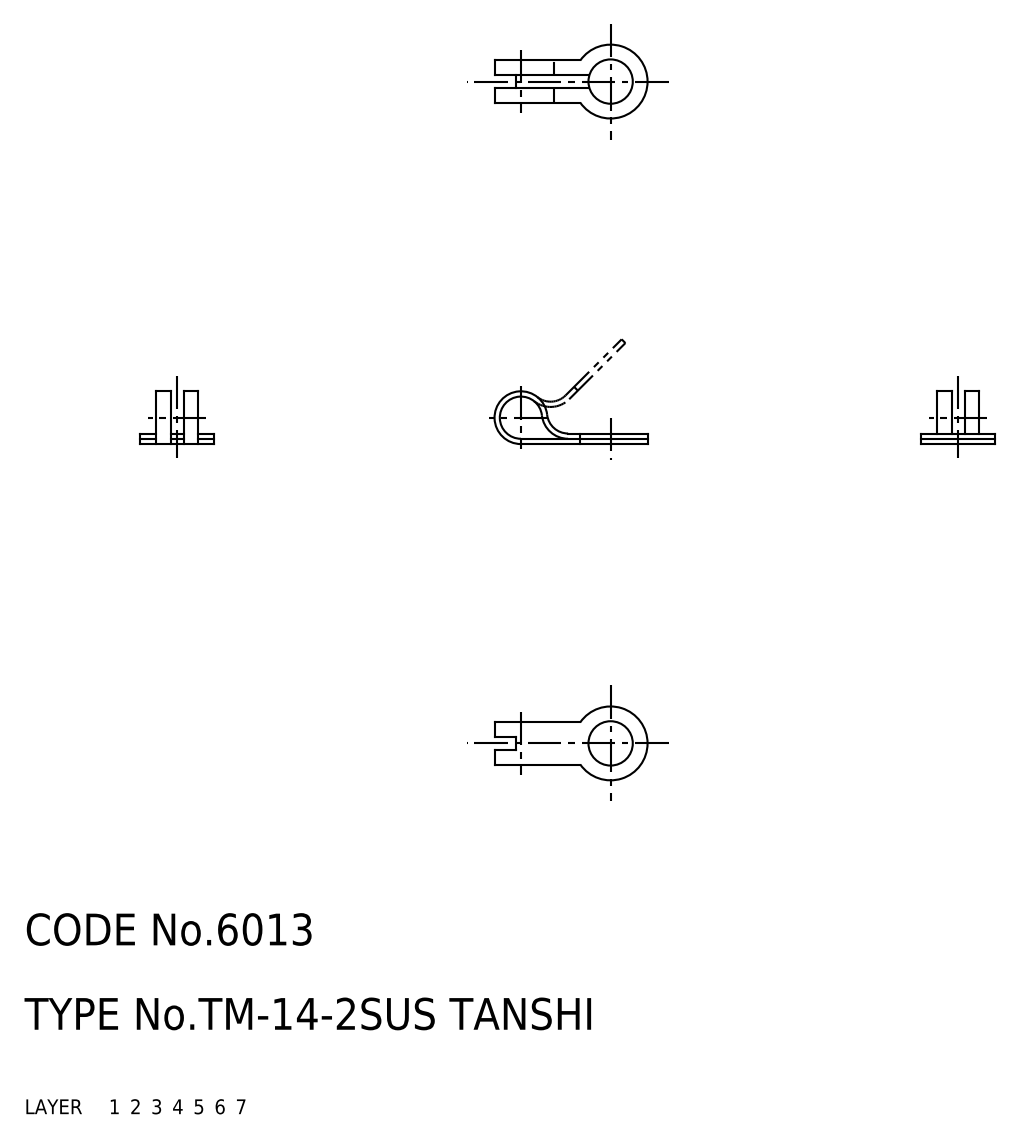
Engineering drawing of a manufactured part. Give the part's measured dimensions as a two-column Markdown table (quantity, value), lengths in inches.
| quantity | value |
| --- | --- |
| part name | terminal |
| STEP written by | CADfix (AUTOMOTIVE_DESIGN) |
| units | inches |
| bodies | 1 solid, 22 faces (0 planar, 0 cylindrical, 22 other) |
| overall size | 0.571 × 0.276 × 0.197 |
| volume | 0.003 in³ |
| surface area | 0.442 in² |
